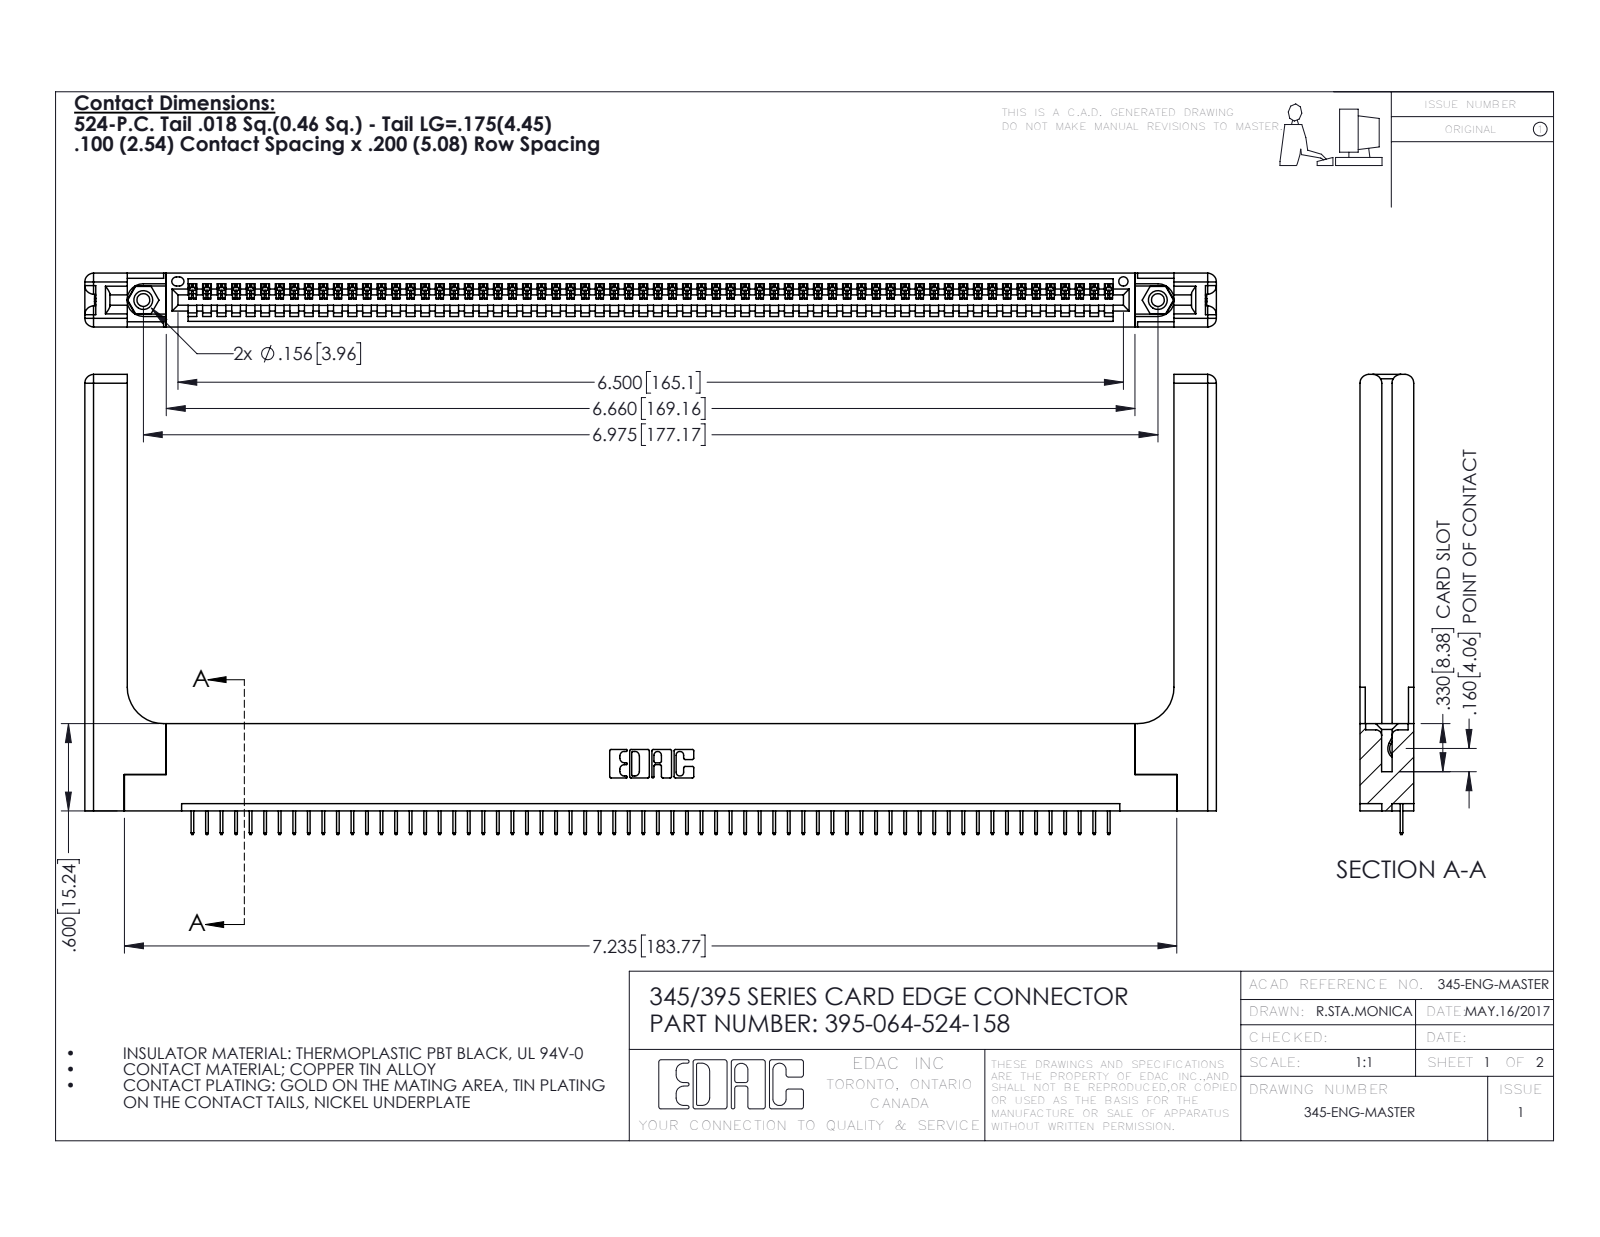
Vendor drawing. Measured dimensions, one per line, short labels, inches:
name: 345-250-001_345-250-001-102; 345-292-001_345-293-124; 395-064-524-158; 345-220-058_345-220-058 (+1 more)
written by: SolidWorks 2016 (CONFIG_CONTROL_DESIGN)
unit: in
bodies: 69 solids, 4350 faces (3172 planar, 1118 cylindrical, 60 other)
size: 7.779 × 3.162 × 0.37
volume: 1.66 in³; area: 45.94 in²
holes: 2× ⌀0.089, 2× ⌀0.125, 2× ⌀0.156, 1× ⌀0.064
bosses: 2× ⌀0.155
rounds: 128× R0.006, 22× R0.01, 16× R0.06, 6× R0.007, 6× R0.031, 3× R0.026, 2× R0.03, 2× R0.031
face distances: 0.072, 0.37, 0.298, 0.2, 0.098, 0.272, 0.025, 0.225, 0.148, 0.15
hole spacings: 0.27, 6.739, 6.975
